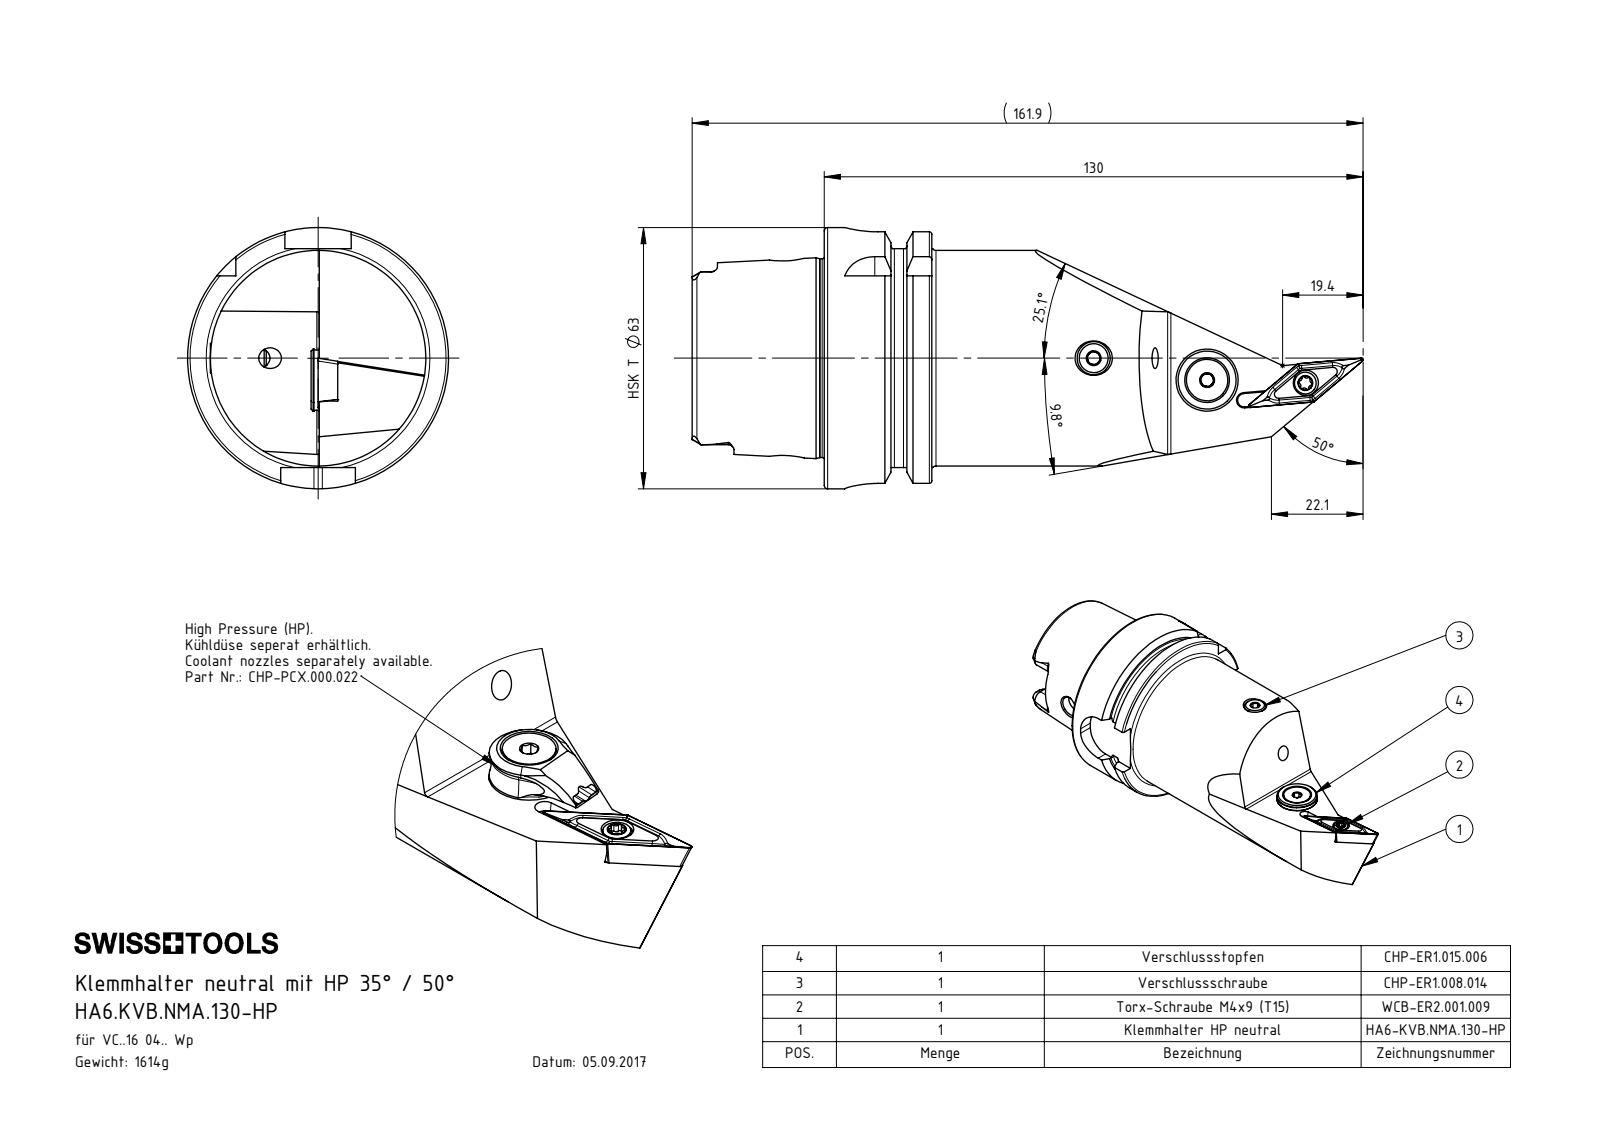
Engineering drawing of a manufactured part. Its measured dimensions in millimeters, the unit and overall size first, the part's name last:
Units: millimetres
Overall size (bounding box): 161.9 × 63 × 63
Round holes (diameter × count): ⌀4.2 ×2, ⌀5 ×2, ⌀1.2 ×1, ⌀2 ×1, ⌀2.5 ×1, ⌀3 ×1, ⌀3.3 ×1, ⌀4.4 ×1, ⌀5.2 ×1, ⌀6.1 ×1, ⌀7 ×1, ⌀7.5 ×1
Round bosses / shafts (diameter × count): ⌀63 ×1, ⌀54.95 ×1, ⌀52 ×1, ⌀47.94 ×1, ⌀15 ×1, ⌀13.4 ×1, ⌀10 ×1, ⌀8 ×1
Partial cylindrical surfaces — rounded edges, fillets, slot ends (radius × count): R0.34 ×6, R0.59 ×6, R1.4 ×6, R2.88 ×4, R8 ×4, R0.8 ×2, R1.6 ×1
Main face-to-face distances: 25.95, 16, 9.95, 31.9, 41.85, 57.85, 52.8, 21.8, 11.85, 4.5
Hole centre spacings: 4.5, 20.84, 20.94, 23.73, 23.84, 27.88, 30.69, 51.44
Volume: 204 976 mm³ · Surface area: 38 809 mm²
Bodies: 8 solids, 425 faces (120 planar, 117 cylindrical, 188 other)
Part name (STEP PRODUCT): WCB-ER2.001.009_A; CHP-ER1.015.006_A; CHP-ER1.008.014_A; HA6-KVB.NMA.130-HP_B (+6 more)
STEP written by: SolidWorks 2017 (AUTOMOTIVE_DESIGN)
